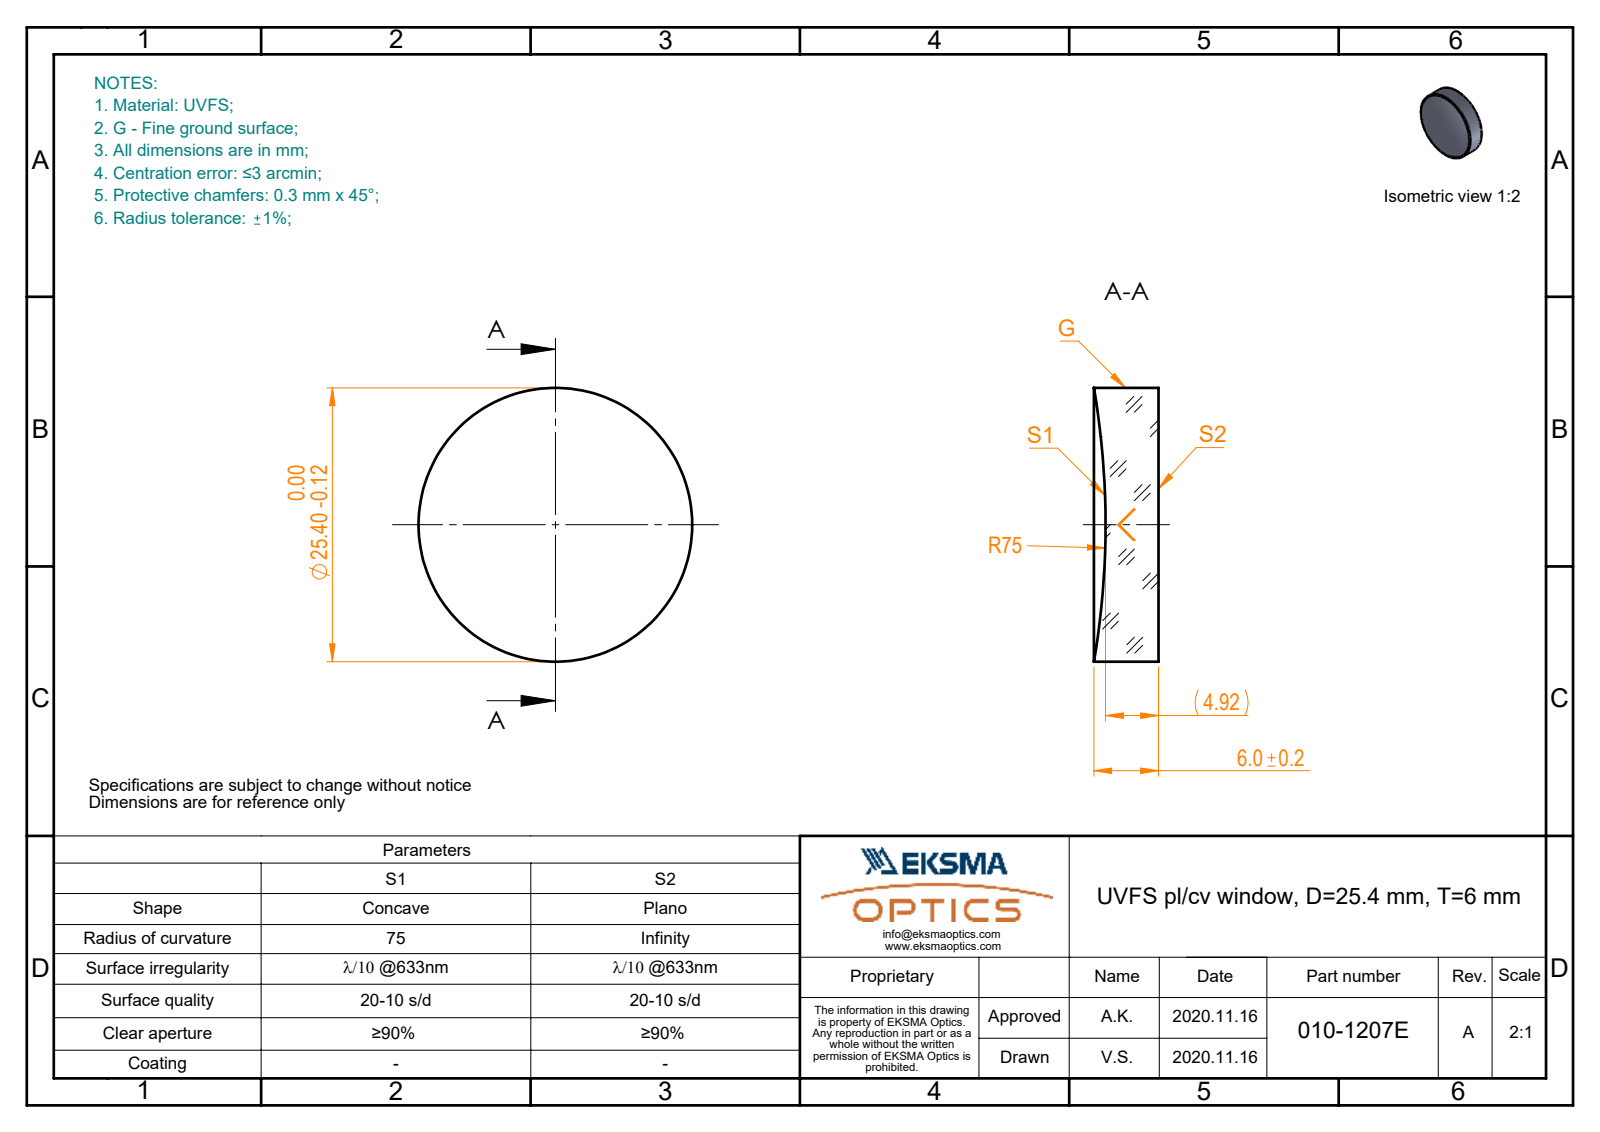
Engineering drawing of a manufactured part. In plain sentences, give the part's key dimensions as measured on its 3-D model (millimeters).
The part is named "010-1207E_UVFS_PCV_window". Its 3-D file was written by "SolidWorks 2019 (CONFIG_CONTROL_DESIGN)". It is 1 solid with 5 faces: 1 planar, 2 cylindrical and 2 other. Overall it measures 25.4 by 25.4 by 6 millimeters. Its volume is 2 765 cubic millimeters and its surface area 1 496 square millimeters. Round bosses or shafts: 1 of diameter 25.4.
